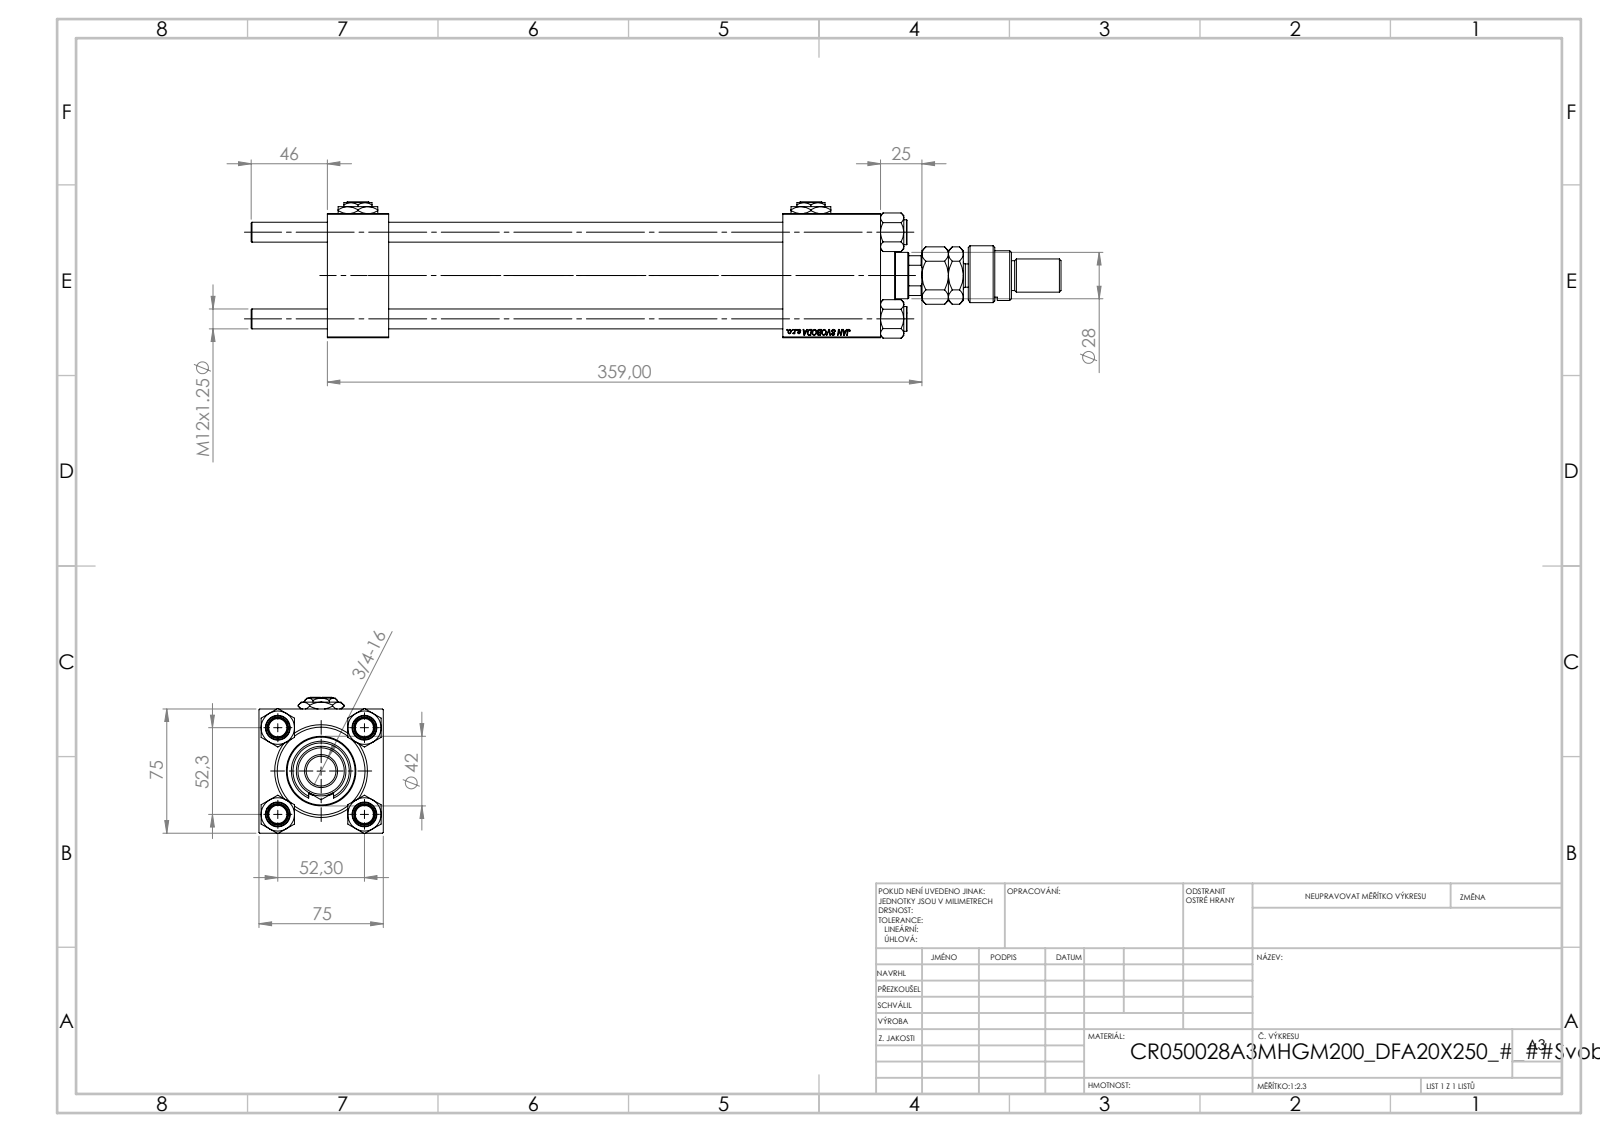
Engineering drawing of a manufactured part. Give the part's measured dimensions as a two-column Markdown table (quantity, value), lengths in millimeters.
| quantity | value |
| --- | --- |
| part name | V215_VC_A; Zatka_pro_OIL_PORT; V215CR_BODY_A; V215CR_VCP (+4 more) |
| STEP written by | SolidWorks 2019 (CONFIG_CONTROL_DESIGN) |
| units | millimeters |
| bodies | 15 solids, 1318 faces (595 planar, 101 cylindrical, 622 other) |
| overall size | 489 × 82.27 × 75 |
| volume | 1 028 000 mm³ |
| surface area | 288 027 mm² |
| round holes (diameter × count) | 12 × 4, 7 × 2, 20.96 × 2, 30 × 2, 18.5 × 1, 28 × 1, 31 × 1, 41 × 1, 50 × 1, 53 × 1 |
| round bosses / shafts (diameter × count) | 15 × 4, 56 × 1, 42 × 1, 36 × 1, 30 × 1, 22 × 1, 20 × 1, 18 × 1 |
| partial cylindrical surfaces (radius × count) | 7.5 × 1, 12 × 1, 13.5 × 1 |
| main face-to-face distances | 75, 37, 334, 297, 275, 59, 238, 305.3, 268.3, 30.3 |
| hole center spacings | 36.98, 52.3, 73.96, 273.5 |
